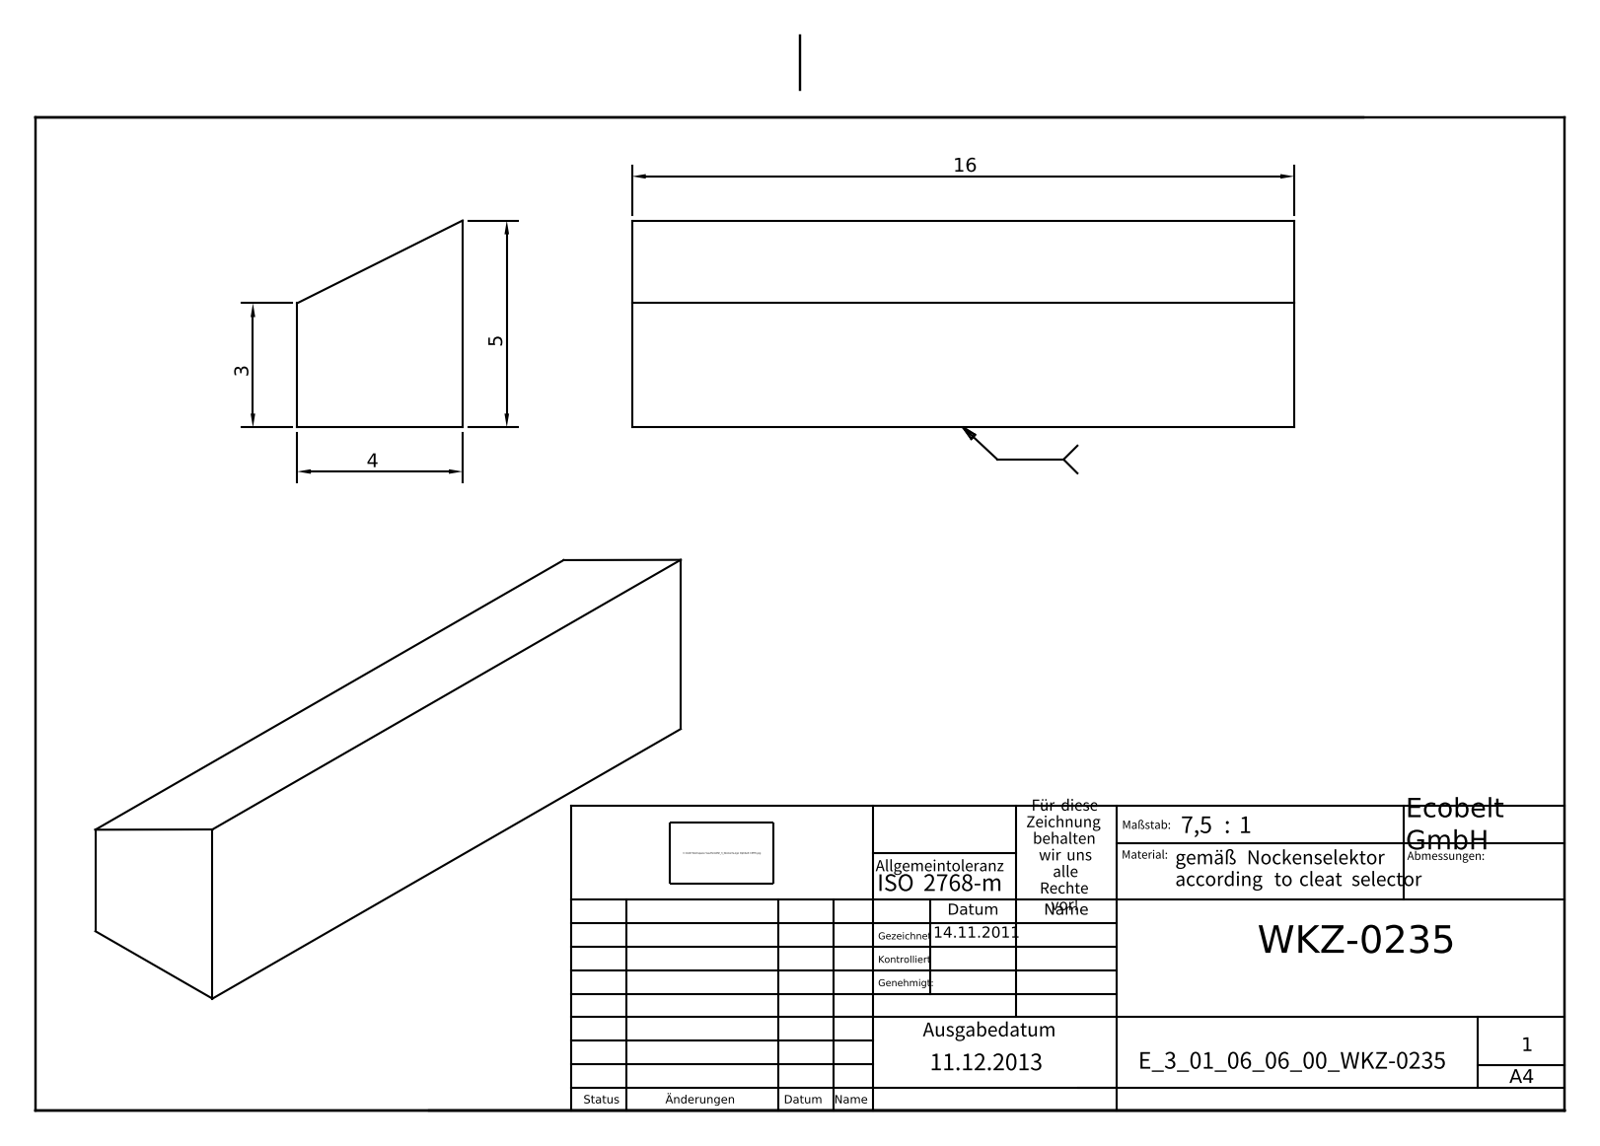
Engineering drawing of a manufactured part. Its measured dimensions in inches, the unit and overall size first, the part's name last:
Units: inches
Overall size (bounding box): 0.63 × 0.197 × 0.157
Main face-to-face distances: 0.157, 0.63
Volume: 0.016 in³ · Surface area: 0.459 in²
Bodies: 1 solid, 6 faces (6 planar, 0 cylindrical, 0 other)
Part name (STEP PRODUCT): E_3_01_06_06_00_WKZ-0235
STEP written by: Autodesk Inventor 2025 (AUTOMOTIVE_DESIGN)
